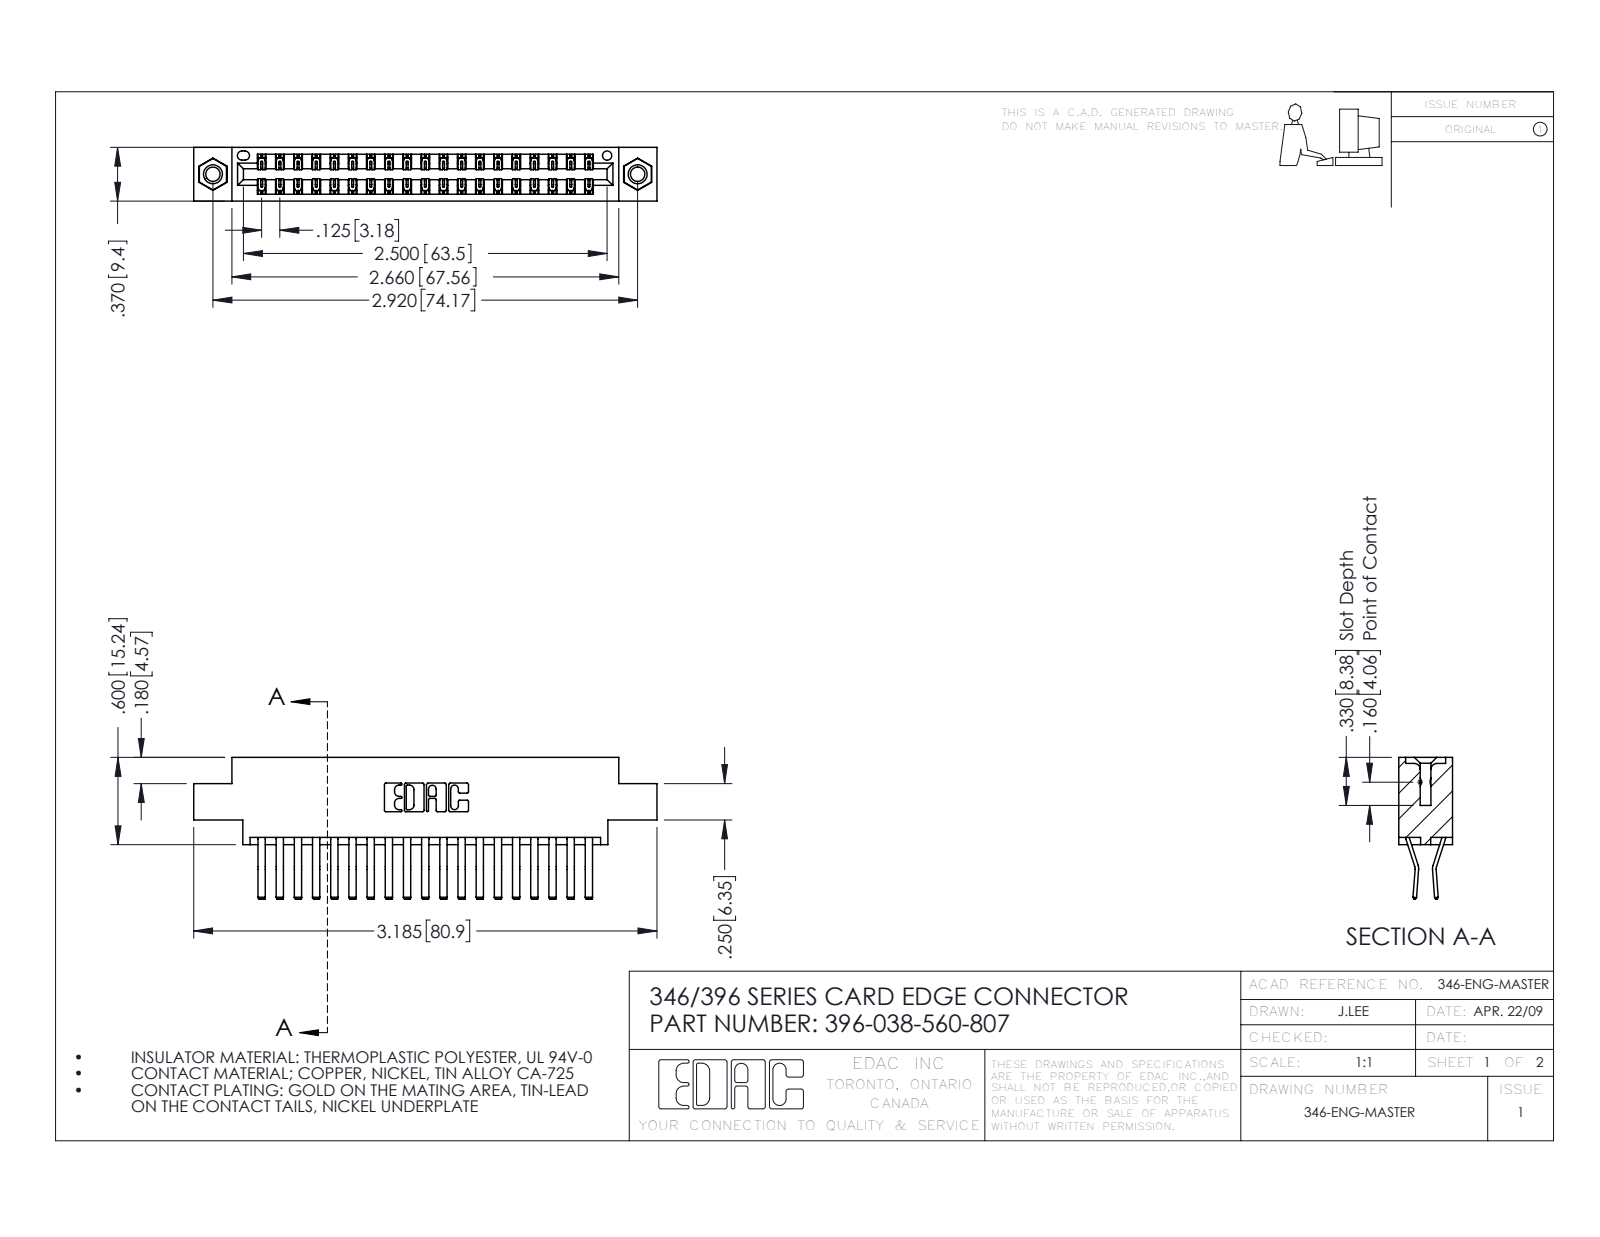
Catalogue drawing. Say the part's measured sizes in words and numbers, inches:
The part is named "345-292-001_560 Tail; 346 Part_0.170 Offset - 0.156 Dia-TI; 345-250-001_345-250-005-103; 396-038-560-807". Its 3-D file was written by "SolidWorks 2016 (CONFIG_CONTROL_DESIGN)". It is 41 solids with 2238 faces: 1442 planar, 780 cylindrical and 16 other. Overall it measures 3.185 by 0.975 by 0.37 inches. Its volume is 0.475 cubic inches and its surface area 17.4 square inches. Round holes: 2 of diameter 0.098, 2 of diameter 0.125, 2 of diameter 0.156, 1 of diameter 0.064. Round bosses or shafts: 2 of diameter 0.155. Partial cylindrical surfaces (rounded edges, fillets, slot ends): 57 of radius 0.006, 22 of radius 0.01, 6 of radius 0.007, 6 of radius 0.031, 3 of radius 0.026, 2 of radius 0.01, 2 of radius 0.014, 2 of radius 0.022. The main face-to-face distances are 0.048, 0.322, 0.37, 0.25, 0.025, 0.072, 0.298, 0.275, 0.222, 0.148. The hole center spacings are 0.246, 2.713, 2.92.
